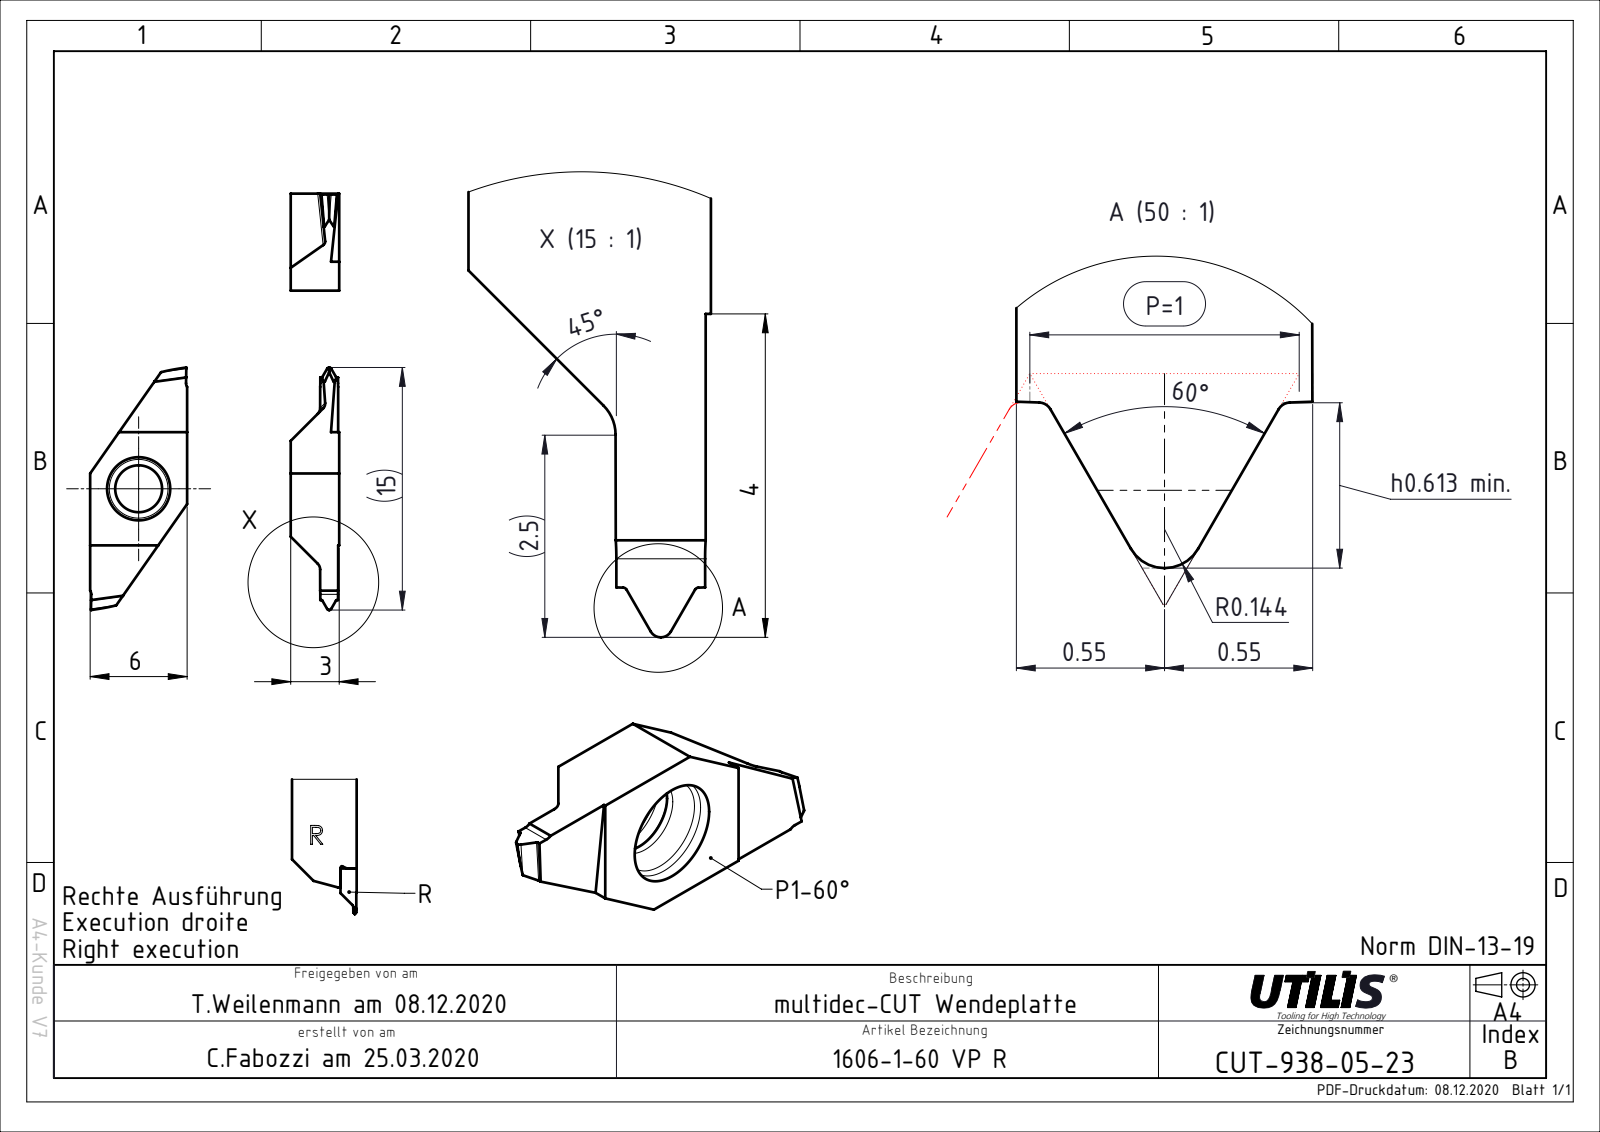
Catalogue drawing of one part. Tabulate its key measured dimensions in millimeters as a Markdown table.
| quantity | value |
| --- | --- |
| part name | CUT-938-05; ASME Y14.5 |
| STEP written by | FormatWorks Professional (AP242_MANAGED_MODEL_BASED_3D_ENGINEERING_MIM_LF) |
| units | millimeters |
| bodies | 1 solid, 38 faces (24 planar, 14 cylindrical, 0 other) |
| overall size | 15 × 6 × 3 |
| volume | 120 mm³ |
| surface area | 208 mm² |
| round holes (diameter × count) | 2.9 × 1 |
| partial cylindrical surfaces (radius × count) | 0.14 × 4, 0.5 × 2 |
| main face-to-face distances | 6, 3, 0.95, 9, 11.26, 11.25, 12, 7, 12.31, 12.32 |
